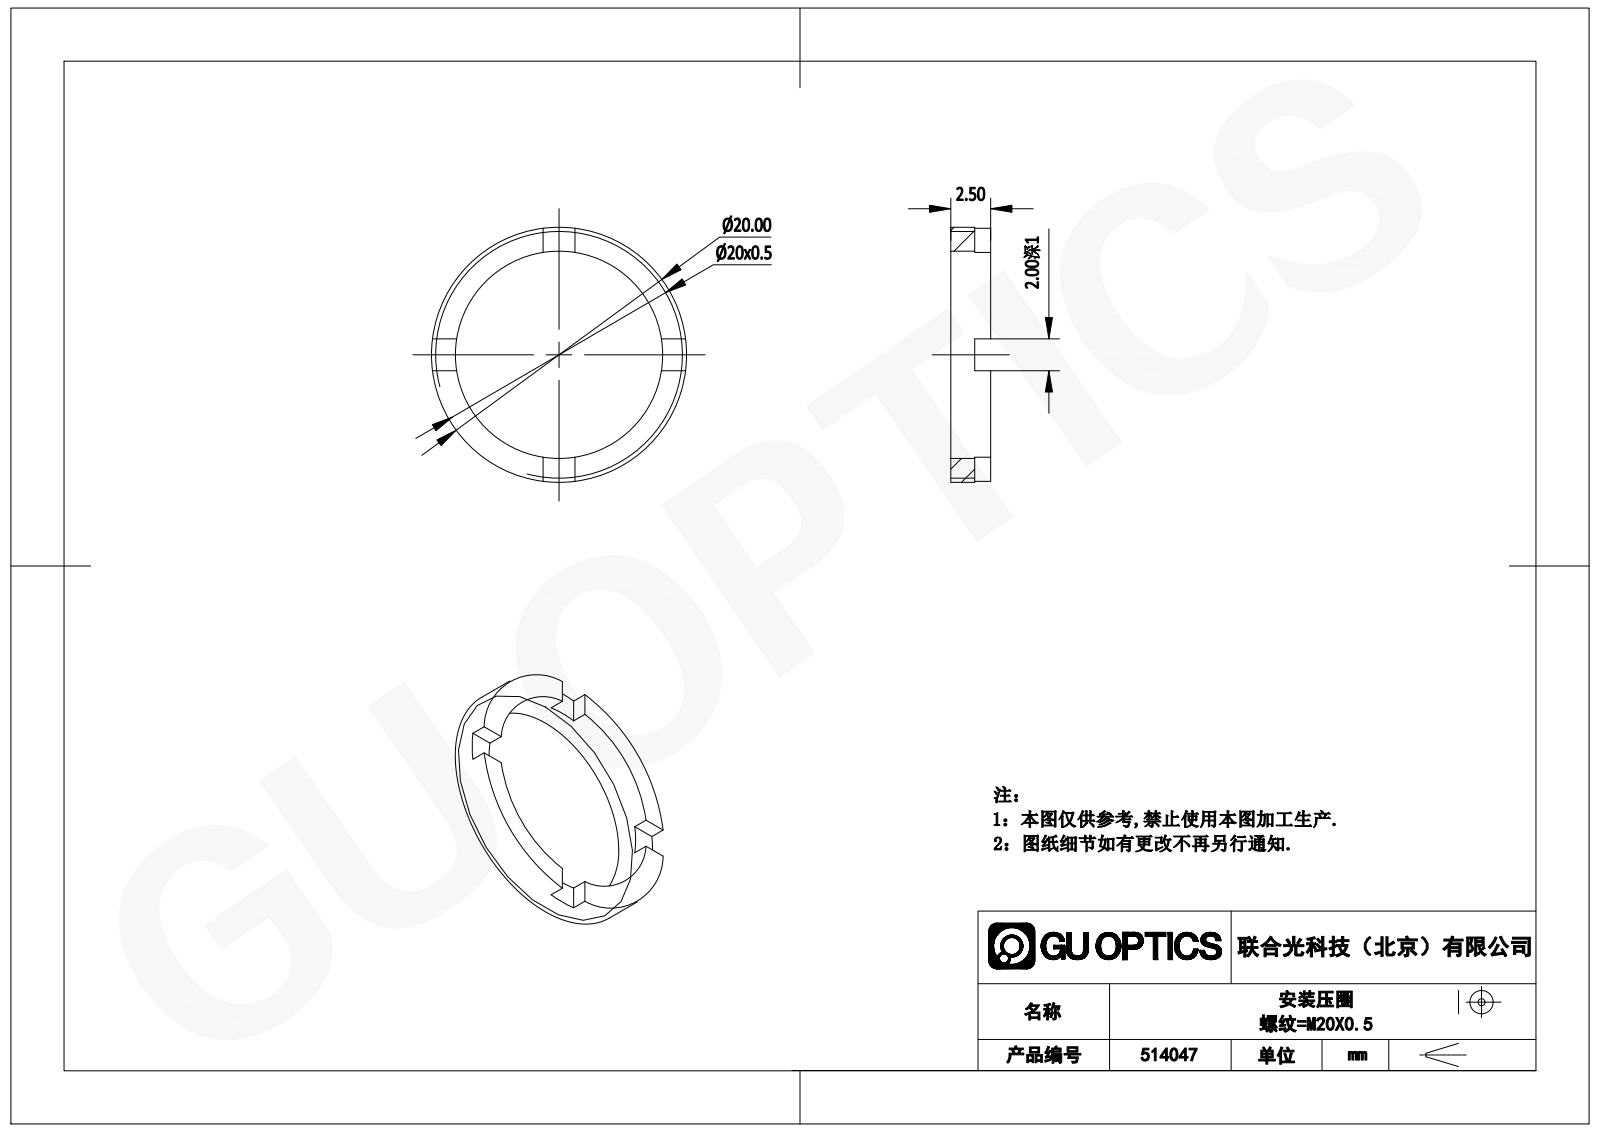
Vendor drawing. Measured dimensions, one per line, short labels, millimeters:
name: 514047
written by: SolidWorks 2020 (CONFIG_CONTROL_DESIGN)
unit: mm
bodies: 1 solid, 21 faces (17 planar, 4 cylindrical, 0 other)
size: 20 × 20 × 2.5
volume: 206 mm³; area: 461 mm²
holes: 1× ⌀17
bosses: 1× ⌀20
face distances: 2.5, 1.5, 1, 2
